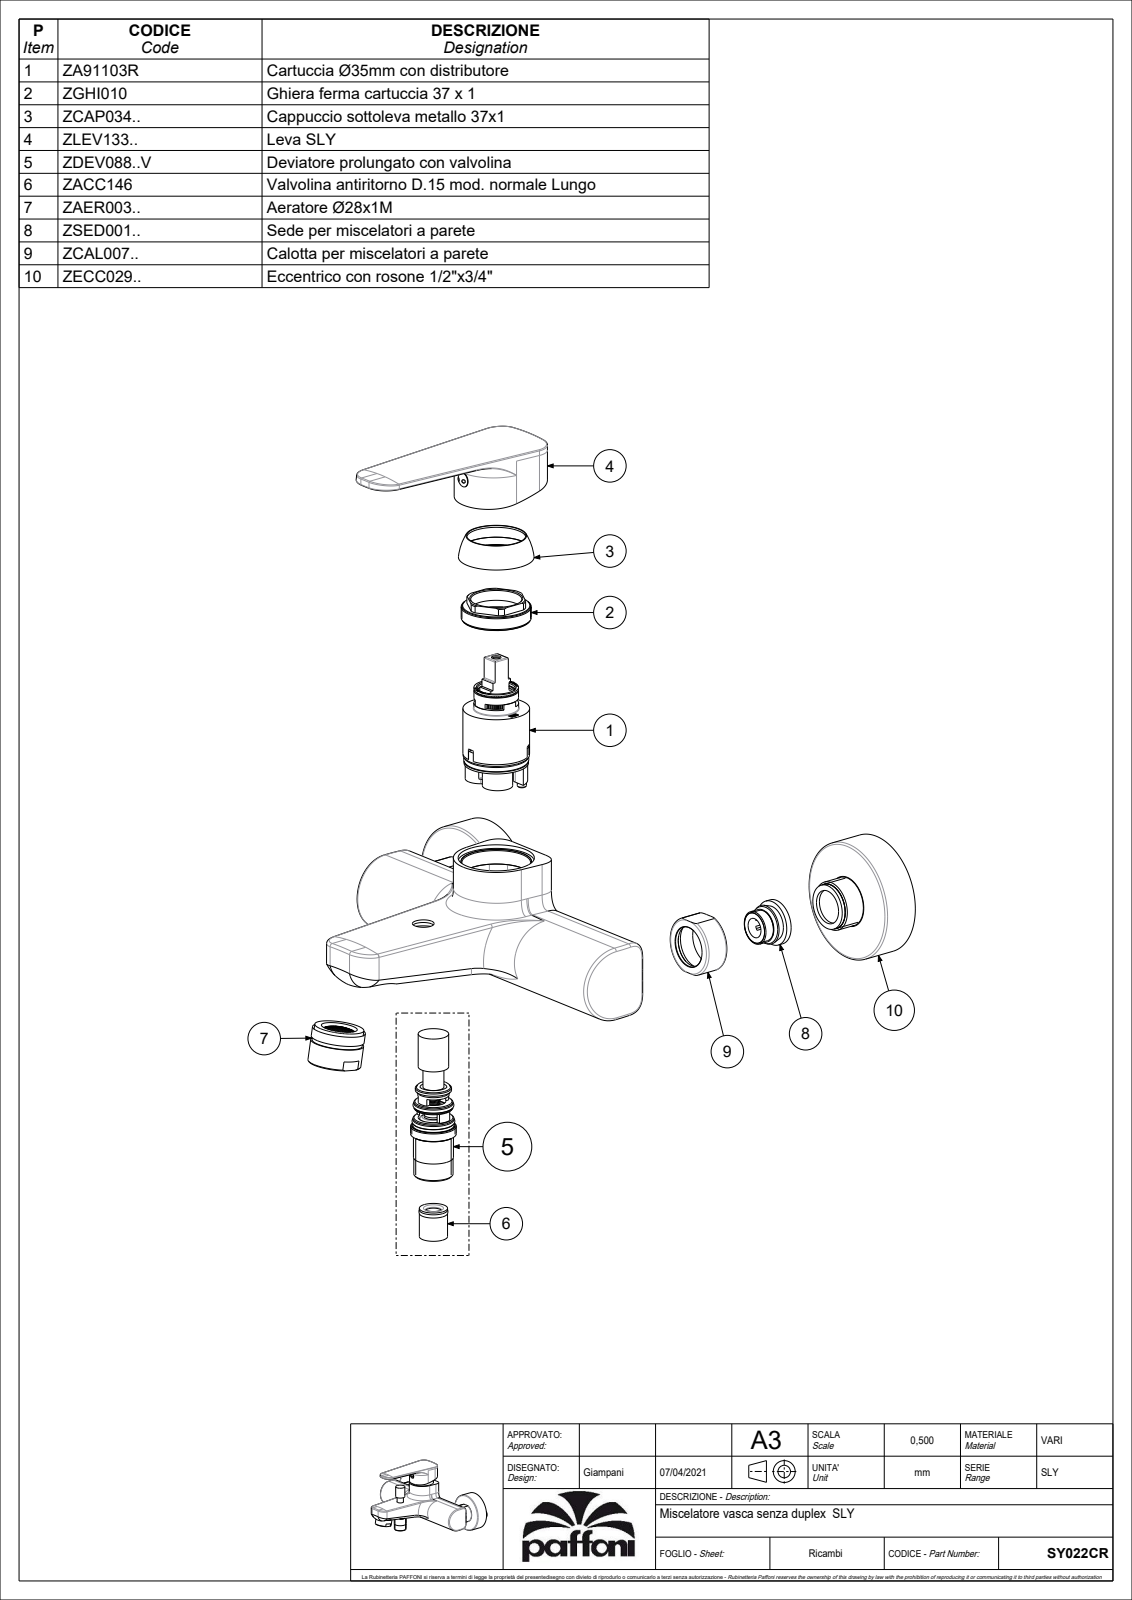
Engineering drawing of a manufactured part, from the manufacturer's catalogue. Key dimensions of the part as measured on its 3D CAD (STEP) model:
Part name (STEP PRODUCT): SY022CR
STEP written by: CREO PARAMETRIC BY PTC INC, 2020044 (CONFIG_CONTROL_DESIGN)
Units: millimetres
Bodies: 3 solids, 3096 faces (2215 planar, 444 cylindrical, 437 other)
Overall size (bounding box): 213.5 × 165 × 109.05
Volume: 260 491 mm³ · Surface area: 175 837 mm²
Round holes (diameter × count): ⌀12 ×4, ⌀9 ×3, ⌀24.5 ×3, ⌀25 ×3, ⌀3.3 ×2, ⌀4 ×2, ⌀5 ×2, ⌀8 ×2, ⌀10.5 ×2, ⌀16.5 ×2, ⌀18 ×2, ⌀19 ×2
Round bosses / shafts (diameter × count): ⌀24 ×3, ⌀63.5 ×2, ⌀27 ×2, ⌀10 ×2, ⌀35 ×1, ⌀34.8 ×1, ⌀33.8 ×1, ⌀32.2 ×1
Partial cylindrical surfaces — rounded edges, fillets, slot ends (radius × count): R0.5 ×44, R0.15 ×11, R0.3 ×9, R1.5 ×6, R1 ×4, R7 ×4, R4.5 ×3, R7.95 ×2
Main face-to-face distances: 3.5, 0.6, 15, 18.5, 3, 15.6, 26.5, 36.5, 19.1, 26
Hole centre spacings: 0.71, 8.51, 8.6, 13.04, 13.21, 13.51, 44.97, 45.54
